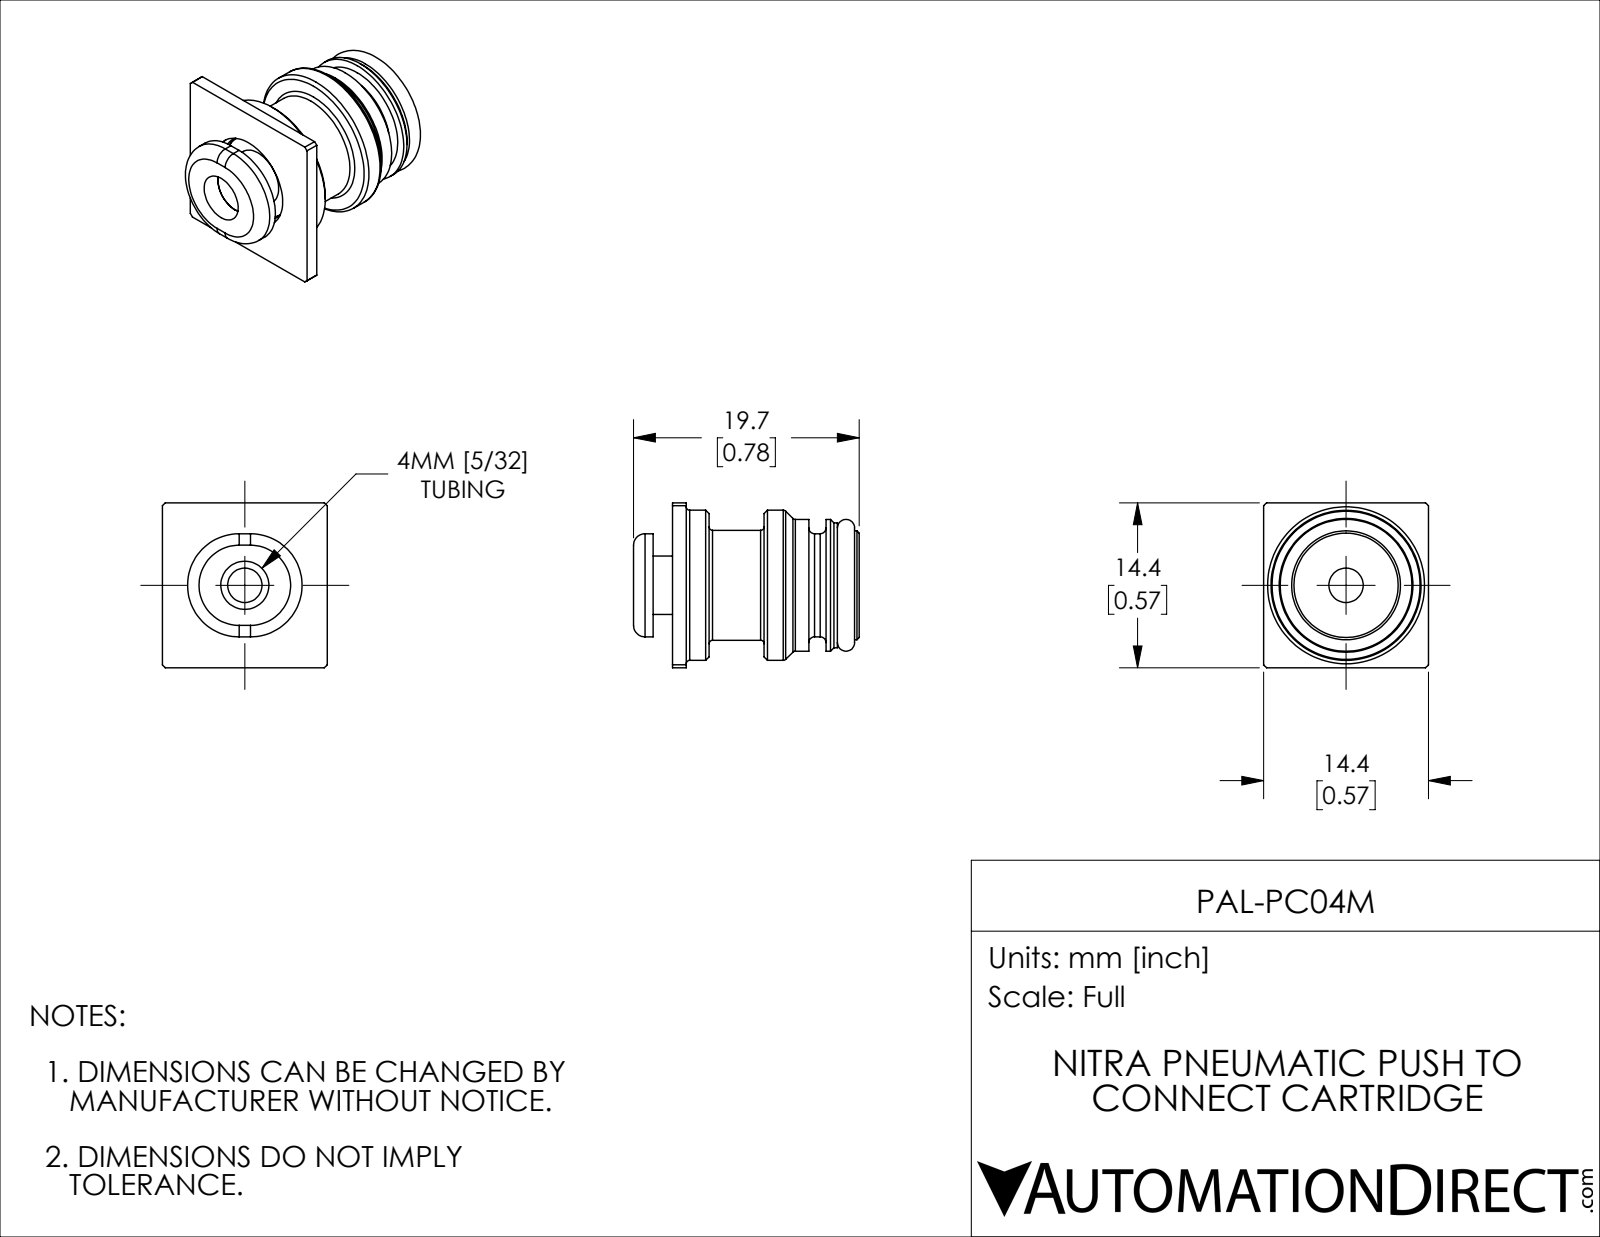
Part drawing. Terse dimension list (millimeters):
name: PAL-PC04M
written by: SolidWorks 2019 (CONFIG_CONTROL_DESIGN)
unit: mm
bodies: 3 solids, 92 faces (20 planar, 38 cylindrical, 34 other)
size: 19.7 × 14.4 × 14.4
volume: 1 625 mm³; area: 1 731 mm²
holes: 1× ⌀3, 1× ⌀4.2, 1× ⌀7.7, 1× ⌀8.39
bosses: 1× ⌀13.1, 1× ⌀11.5, 1× ⌀10.9, 1× ⌀9.6, 1× ⌀9.5, 1× ⌀9, 1× ⌀8.5, 1× ⌀5.1
rounds: 2× R1, 2× R4.5, 1× R10
face distances: 1.7, 2.9, 15.1, 14.4, 1.2, 16.3, 18, 3.2, 4.8, 8.3
